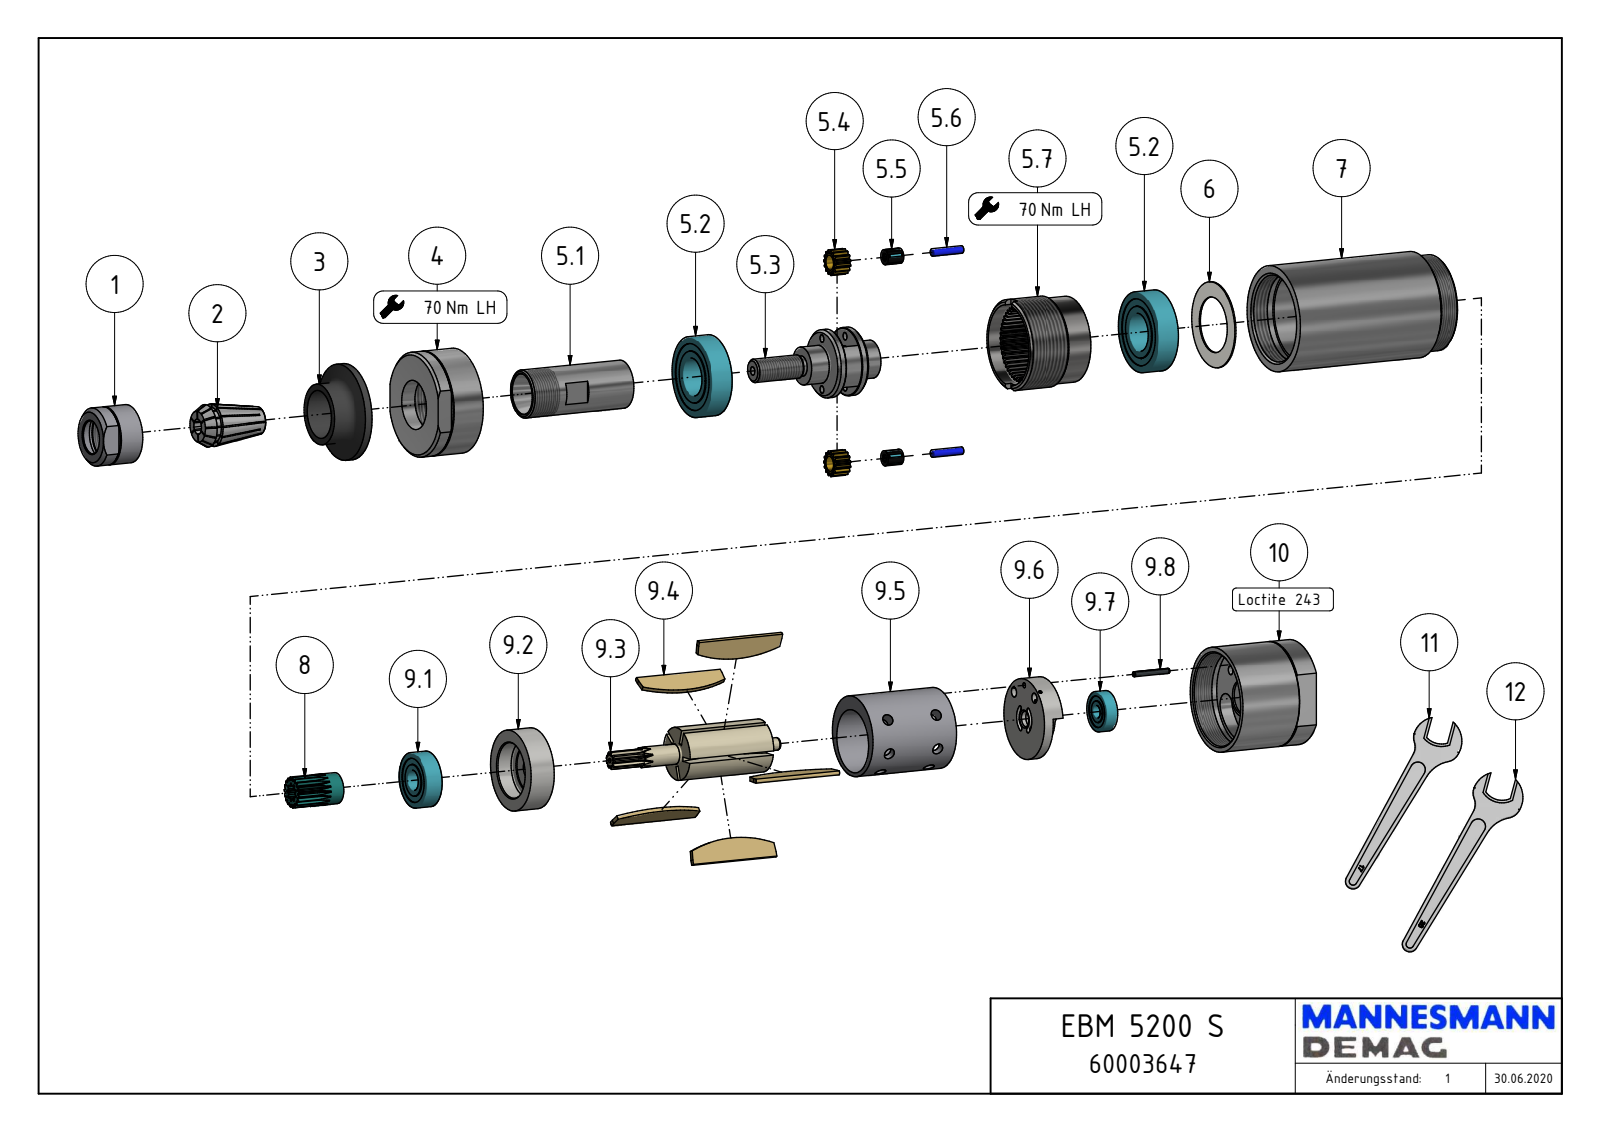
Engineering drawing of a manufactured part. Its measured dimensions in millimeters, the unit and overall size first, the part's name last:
Units: millimetres
Overall size (bounding box): 168.42 × 42 × 42
Round holes (diameter × count): ⌀11.45 ×2, ⌀1.6 ×1, ⌀6 ×1, ⌀10.5 ×1, ⌀17.92 ×1, ⌀19 ×1
Round bosses / shafts (diameter × count): ⌀42 ×1, ⌀41.5 ×1, ⌀38 ×1, ⌀36 ×1, ⌀24 ×1, ⌀23 ×1, ⌀18.98 ×1, ⌀14 ×1
Partial cylindrical surfaces — rounded edges, fillets, slot ends (radius × count): R18.09 ×6, R33.72 ×6
Main face-to-face distances: 0.5, 99, 1.5, 100.5, 37, 9, 1, 17, 11.95, 88.55
Hole centre spacings: 10.5, 11.72, 20.12
Volume: 178 743 mm³ · Surface area: 27 490 mm²
Bodies: 1 solid, 238 faces (145 planar, 40 cylindrical, 53 other)
Part name (STEP PRODUCT): EBM 5200 S_60003647
STEP written by: Autodesk Inventor 2012 (AUTOMOTIVE_DESIGN)
